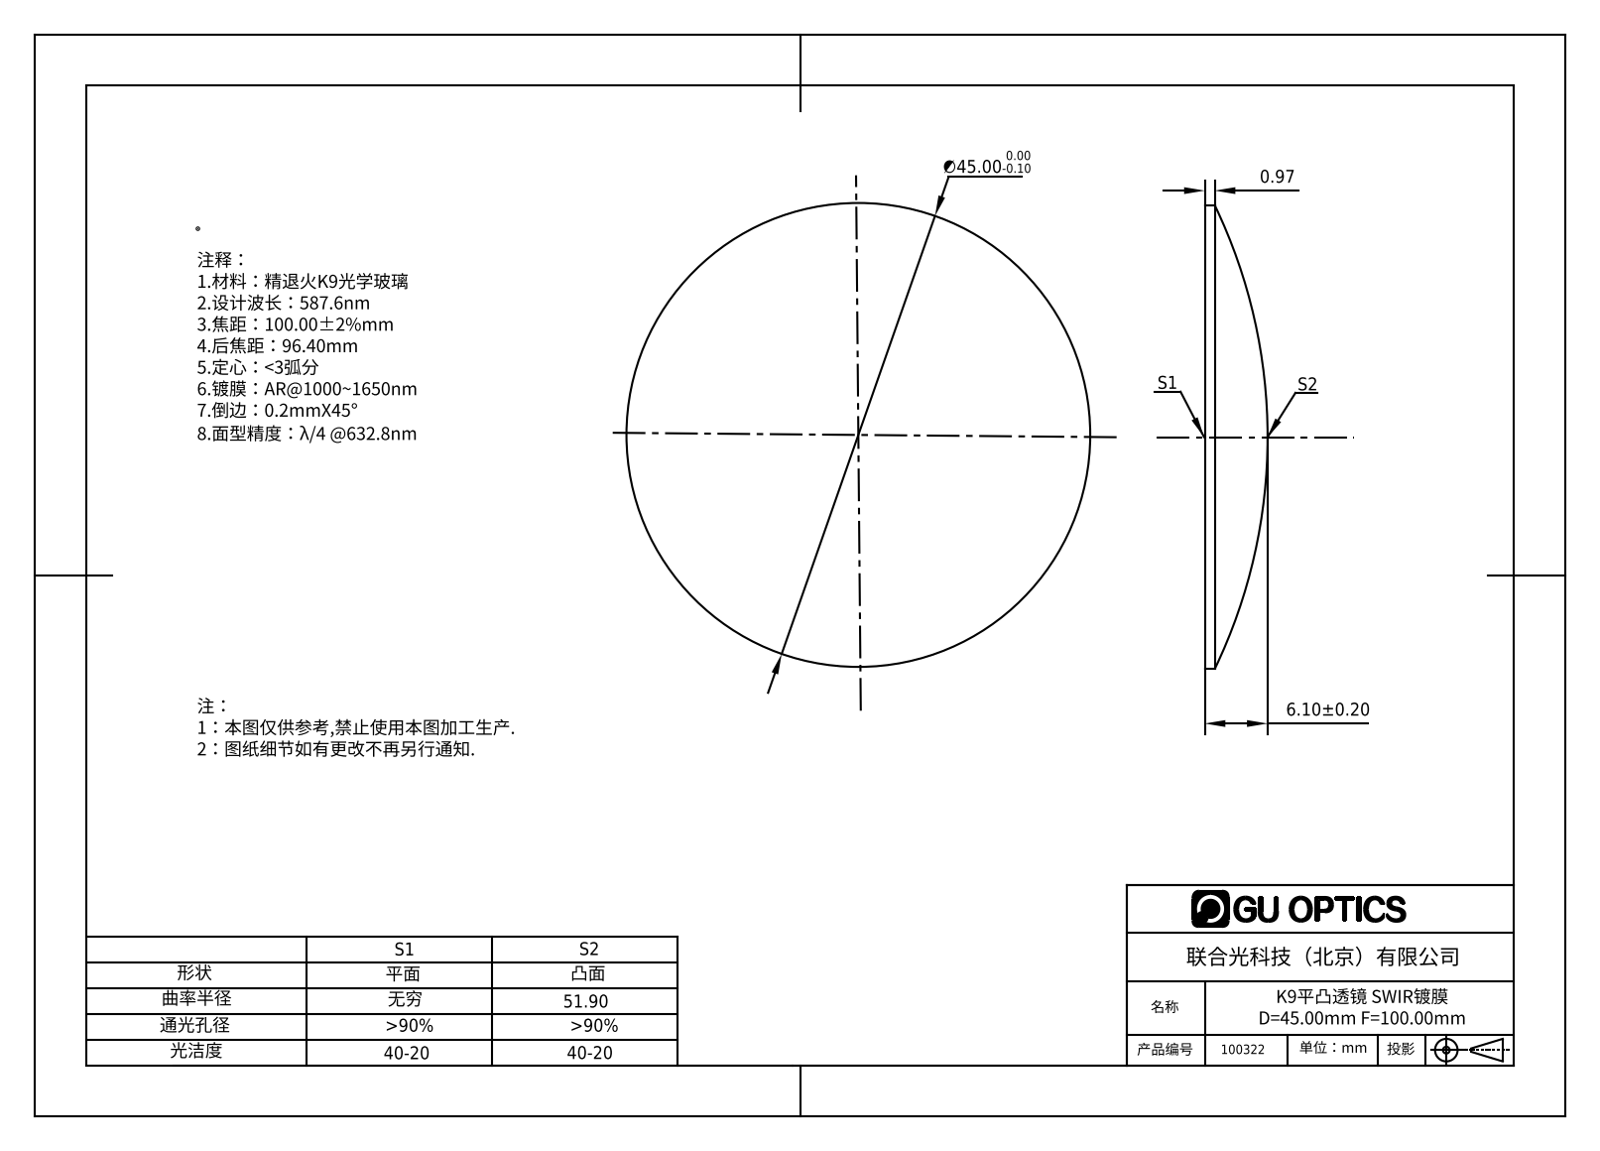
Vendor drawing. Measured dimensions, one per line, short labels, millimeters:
name: 100150
written by: SolidWorks 2016 (AUTOMOTIVE_DESIGN)
unit: mm
bodies: 1 solid, 5 faces (1 planar, 2 cylindrical, 2 other)
size: 45 × 45 × 6.1
volume: 5 693 mm³; area: 3 401 mm²
bosses: 1× ⌀45
